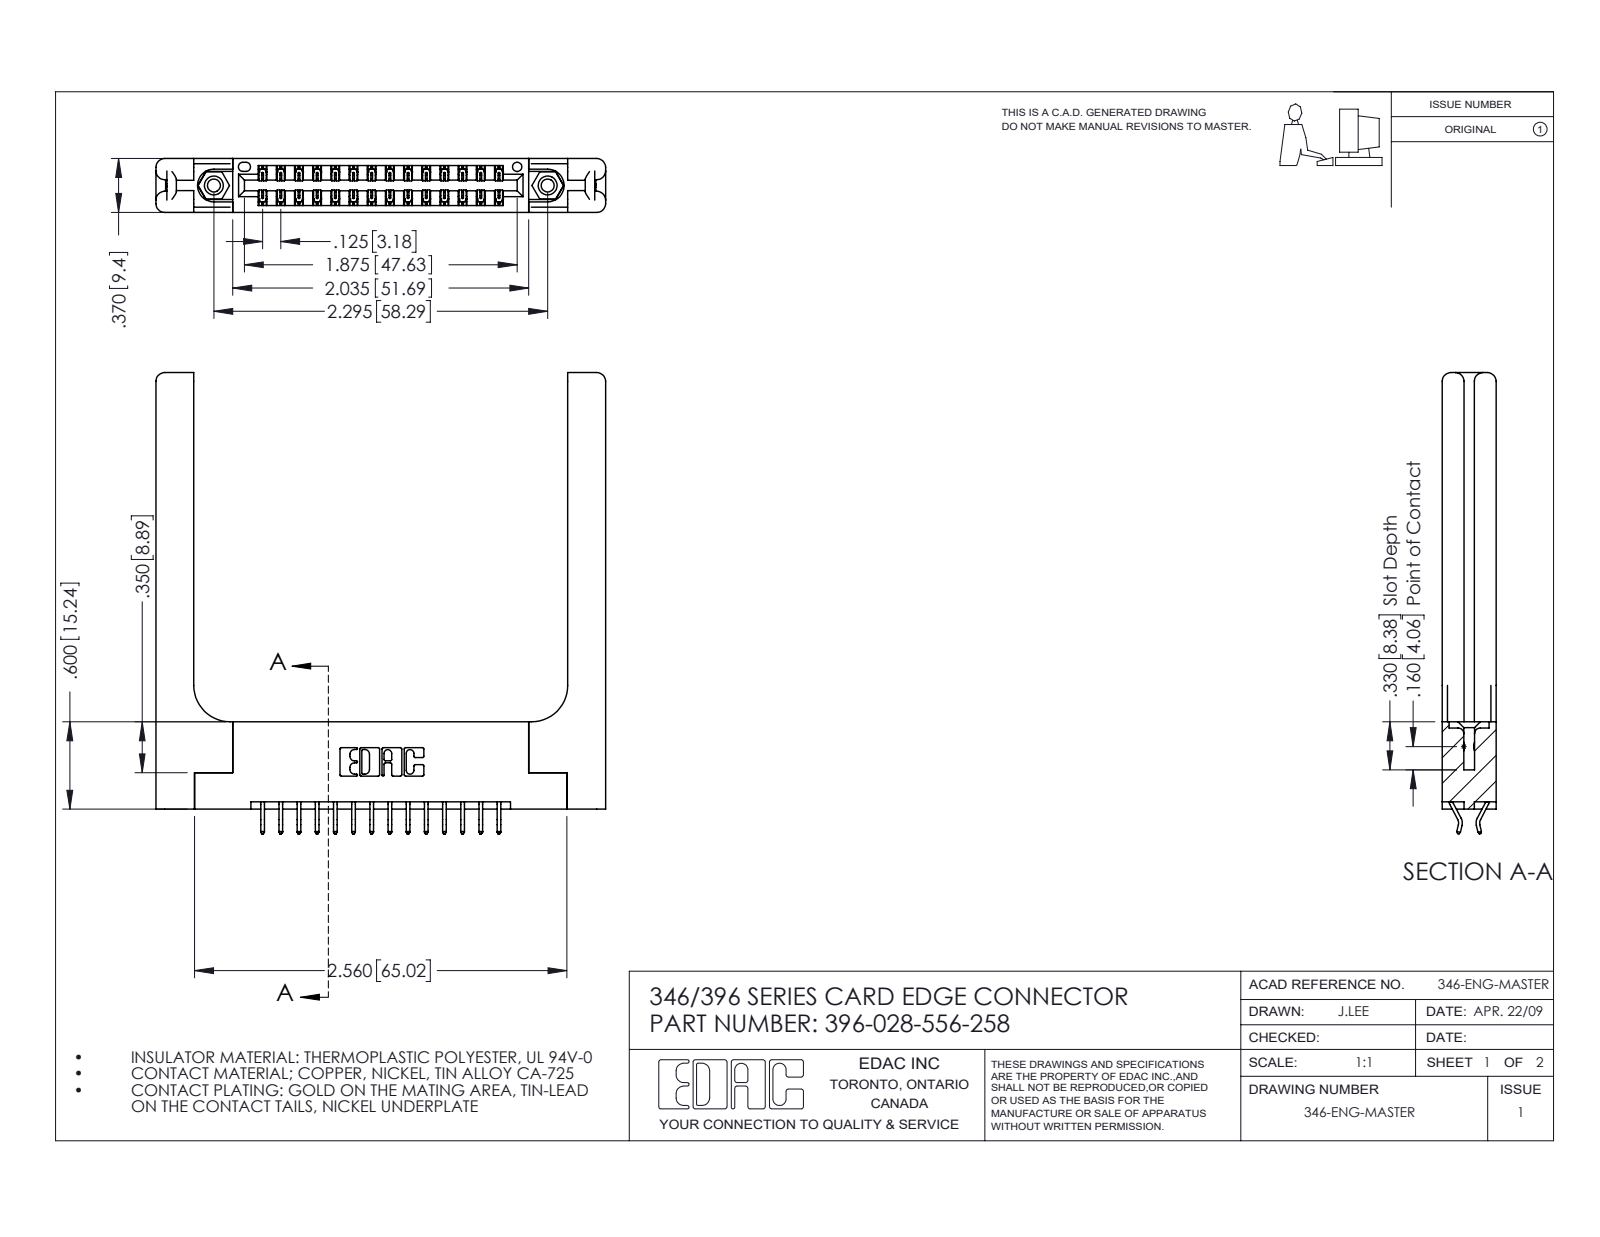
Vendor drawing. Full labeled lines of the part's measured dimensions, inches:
Part name (STEP PRODUCT): 345-292-001_556 Tail; 345-250-001_345-250-001-102; 346 Part_Flush Mounting Lugs - 0.156 Dia-TH; 346-220-058_345-220-058 (+1 more)
STEP written by: SolidWorks 2016 (CONFIG_CONTROL_DESIGN)
Units: inches
Bodies: 33 solids, 2002 faces (1316 planar, 626 cylindrical, 60 other)
Overall size (bounding box): 3.17 × 3.091 × 0.37
Volume: 0.911 in³ · Surface area: 22.83 in²
Round holes (diameter × count): ⌀0.089 ×2, ⌀0.125 ×2, ⌀0.156 ×2, ⌀0.064 ×1
Round bosses / shafts (diameter × count): ⌀0.155 ×2
Partial cylindrical surfaces — rounded edges, fillets, slot ends (radius × count): R0.006 ×42, R0.01 ×22, R0.06 ×16, R0.007 ×6, R0.031 ×6, R0.026 ×3, R0.01 ×2, R0.014 ×2
Main face-to-face distances: 0.37, 0.15, 0.072, 0.148, 0.048, 0.322, 0.25, 0.102, 0.22, 0.173
Hole centre spacings: 0.246, 2.089, 2.295
